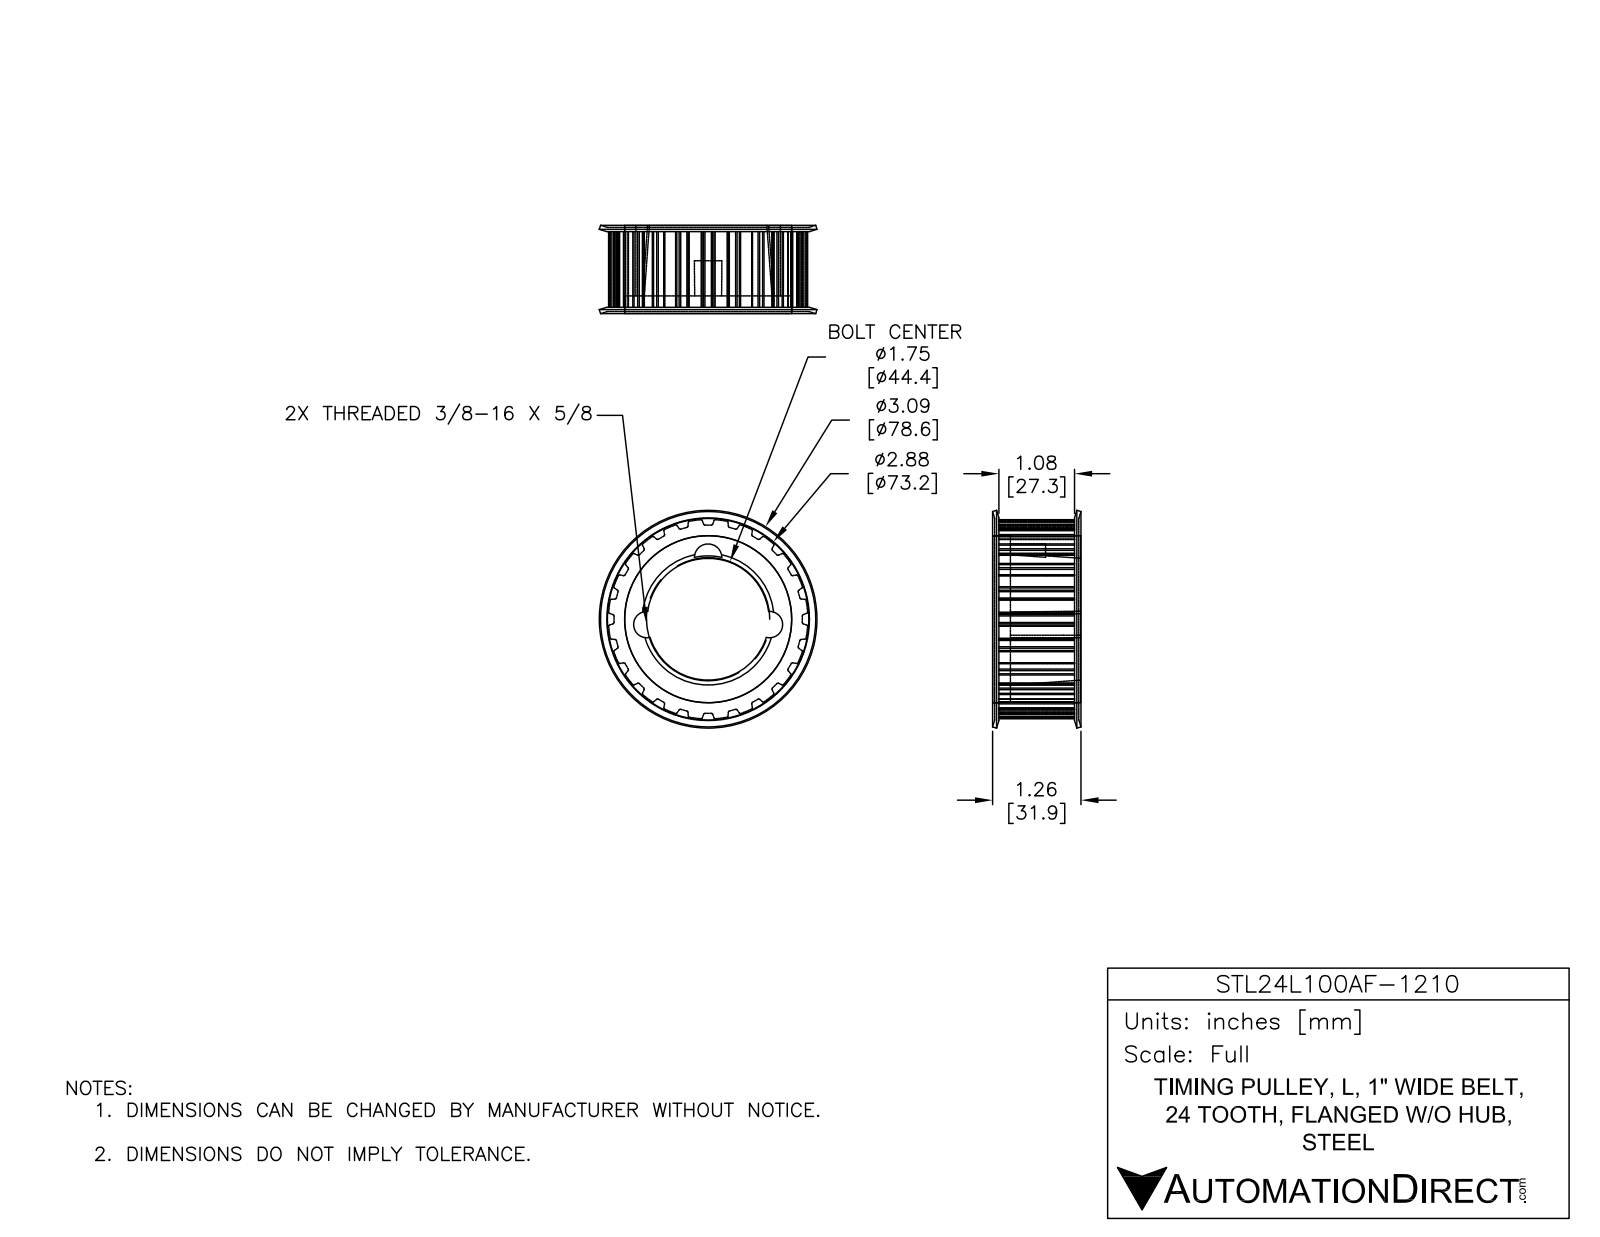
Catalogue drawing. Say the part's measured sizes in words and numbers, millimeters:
The part is named "STL24L100AF-1210". Its 3-D file was written by "SolidWorks 2018 (AUTOMOTIVE_DESIGN)". It is 4 solids with 252 faces: 82 planar, 152 cylindrical and 18 other. Overall it measures 78.58 by 78.58 by 29.66 millimeters. Its volume is 63 149 cubic millimeters and its surface area 35 804 square millimeters. Round holes: 1 of diameter 55.54, 1 of diameter 60.24, 1 of diameter 60.32. Partial cylindrical surfaces (rounded edges, fillets, slot ends): 48 of radius 0.38, 48 of radius 0.51, 2 of radius 3.94, 1 of radius 4.95, 1 of radius 36, 1 of radius 36.01. The main face-to-face distances are 25.09, 2.22, 27.31, 1.52, 26.61, 28.14, 28.83, 26.62, 1.53, 0.69.
